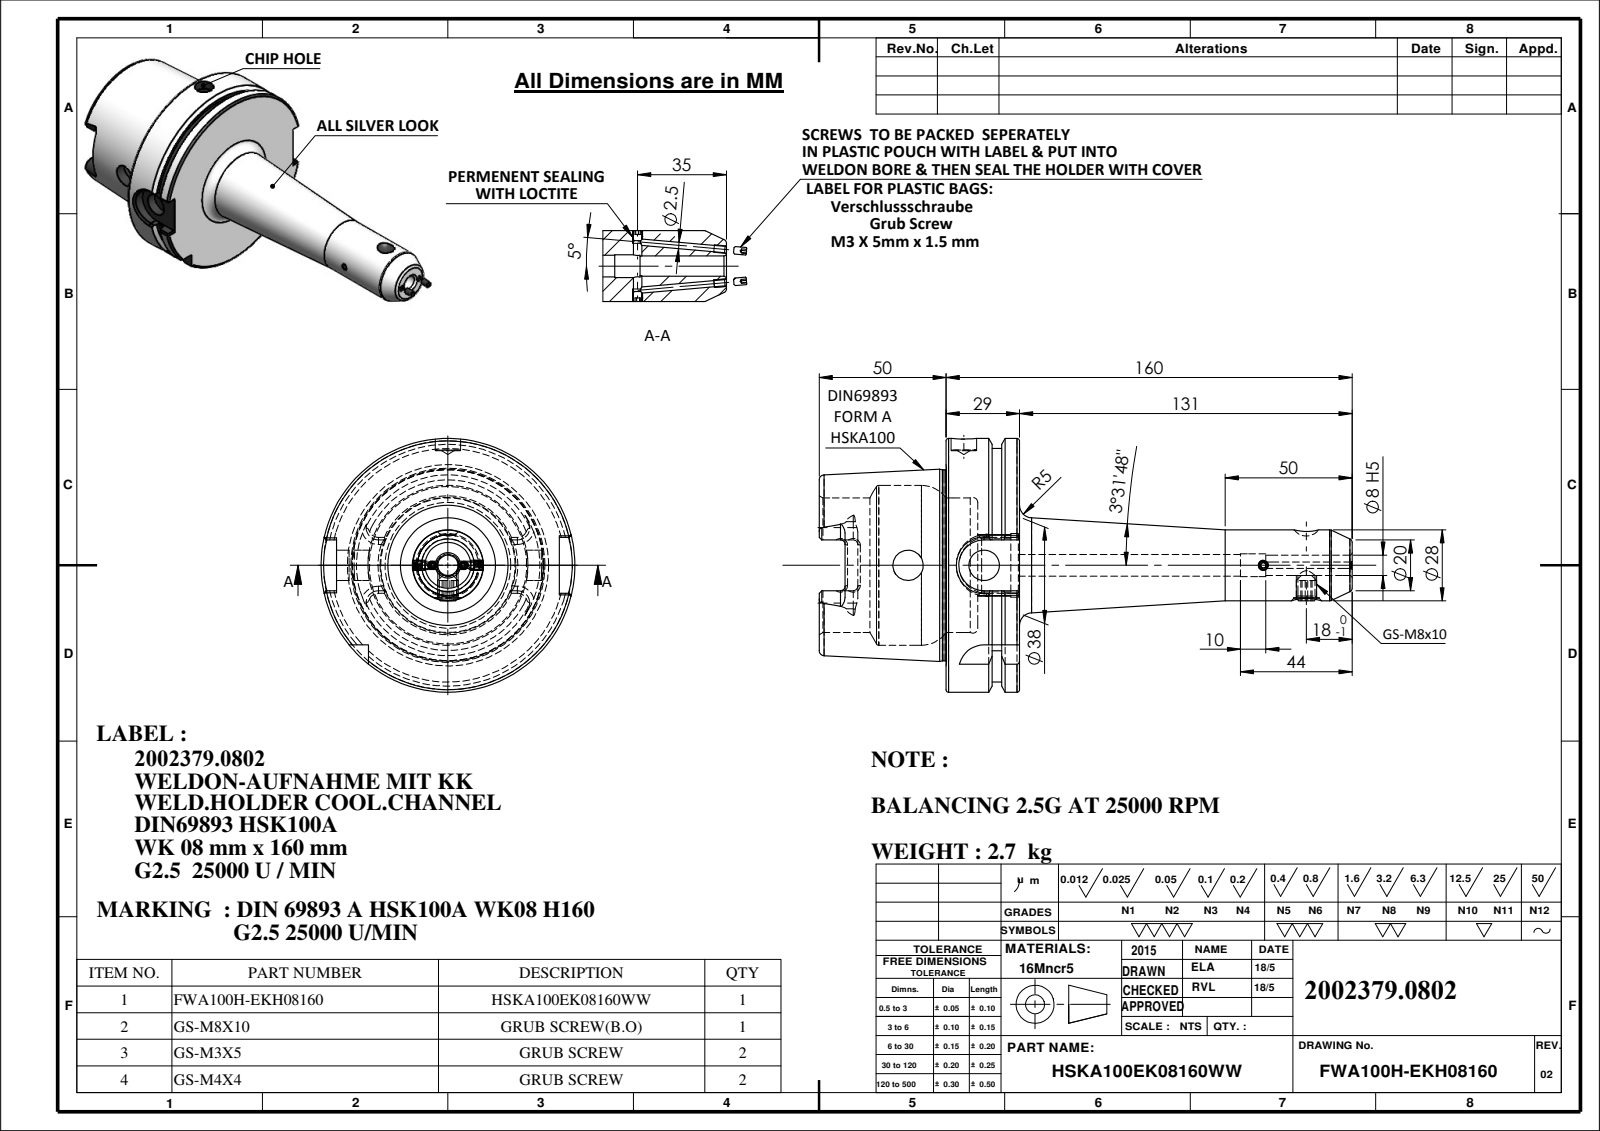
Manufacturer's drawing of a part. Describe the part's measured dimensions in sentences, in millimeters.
The part is named "GS-M4X4_DIN 913 - M4 x 4-N; GS-M8X10-DIN1835-B; HSKA100EK08160WW-R02; GS-M3X5 (+2 more)". Its 3-D file was written by "SolidWorks 2018 (CONFIG_CONTROL_DESIGN)". It is 6 solids with 353 faces: 107 planar, 90 cylindrical and 156 other. Overall it measures 218 by 100 by 100 millimeters. Its volume is 345 718 cubic millimeters and its surface area 66 525 square millimeters. Round holes: 2 of diameter 2.5, 2 of diameter 10, 2 of diameter 12, 1 of diameter 3.3, 1 of diameter 6.8, 1 of diameter 8, 1 of diameter 8.5, 1 of diameter 9, 1 of diameter 21, 1 of diameter 25, 1 of diameter 53, 1 of diameter 63. Round bosses or shafts: 2 of diameter 3, 1 of diameter 100, 1 of diameter 92, 1 of diameter 75.16, 1 of diameter 28, 1 of diameter 8, 1 of diameter 4. Partial cylindrical surfaces (rounded edges, fillets, slot ends): 6 of radius 1.8, 4 of radius 4.88, 2 of radius 10, 1 of radius 11. The main face-to-face distances are 28.95, 12.5, 16.45, 50, 62.5, 78.95, 16, 78.5, 28.5, 0.45. The hole center spacings are 30, 110, 135, 140.
